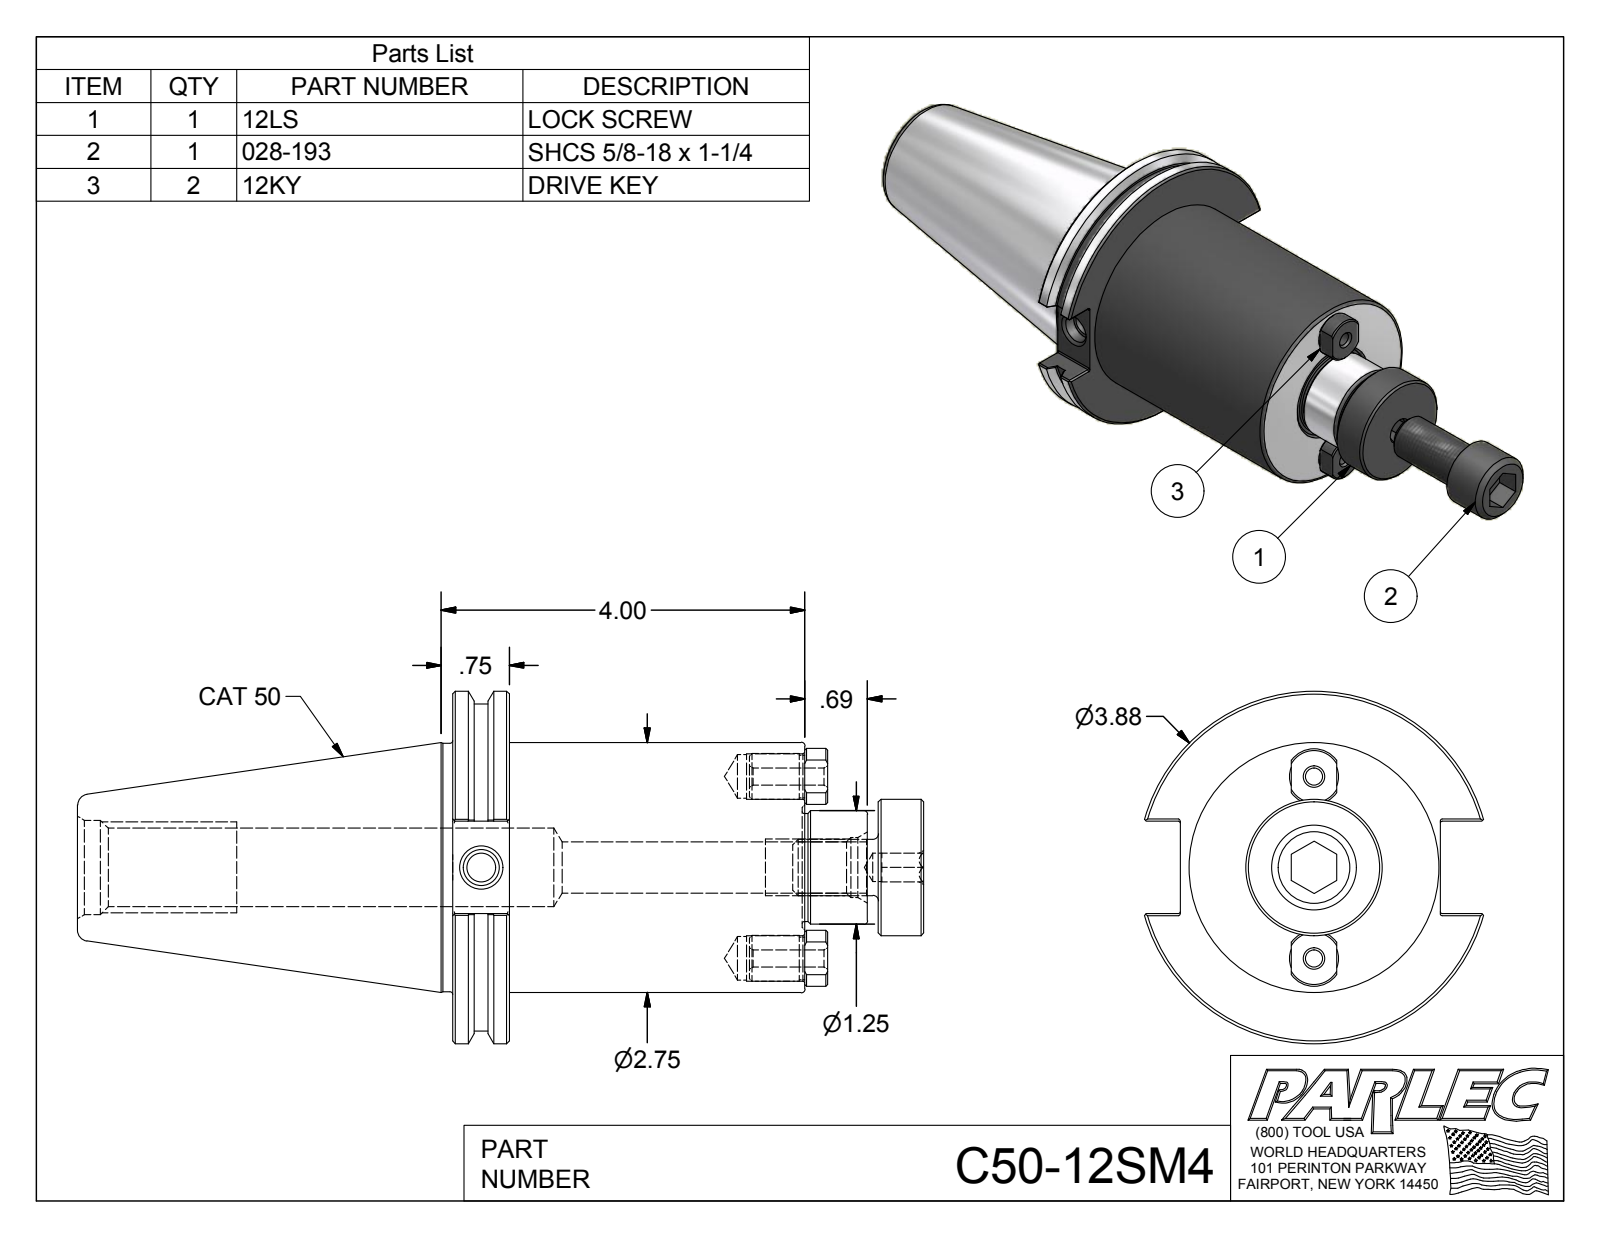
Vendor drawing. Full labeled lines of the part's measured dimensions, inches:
Part name (STEP PRODUCT): C50-12SM4; C50-12SM4-1; 12KY; 12LS (+1 more)
STEP written by: Autodesk Inventor 2012 (AUTOMOTIVE_DESIGN)
Units: inches
Bodies: 5 solids, 172 faces (67 planar, 47 cylindrical, 58 other)
Overall size (bounding box): 11.307 × 3.875 × 3.729
Volume: 40.16 in³ · Surface area: 127.9 in²
Round holes (diameter × count): ⌀0.19 ×2, ⌀0.48 ×2, ⌀0.5 ×2, ⌀0.312 ×1, ⌀0.315 ×1, ⌀0.399 ×1, ⌀0.565 ×1, ⌀0.66 ×1, ⌀0.865 ×1, ⌀1.038 ×1
Round bosses / shafts (diameter × count): ⌀0.505 ×2, ⌀0.47 ×2, ⌀3.875 ×1, ⌀3.594 ×1, ⌀2.75 ×1, ⌀2.73 ×1, ⌀1.5 ×1, ⌀1.25 ×1
Partial cylindrical surfaces — rounded edges, fillets, slot ends (radius × count): R0.02 ×12, R0.308 ×2
Main face-to-face distances: 0.625, 3.875, 3.25, 5.182, 4.557, 1.307, 0.5, 4.682, 4.057, 0.807
Hole centre spacings: 1, 2
